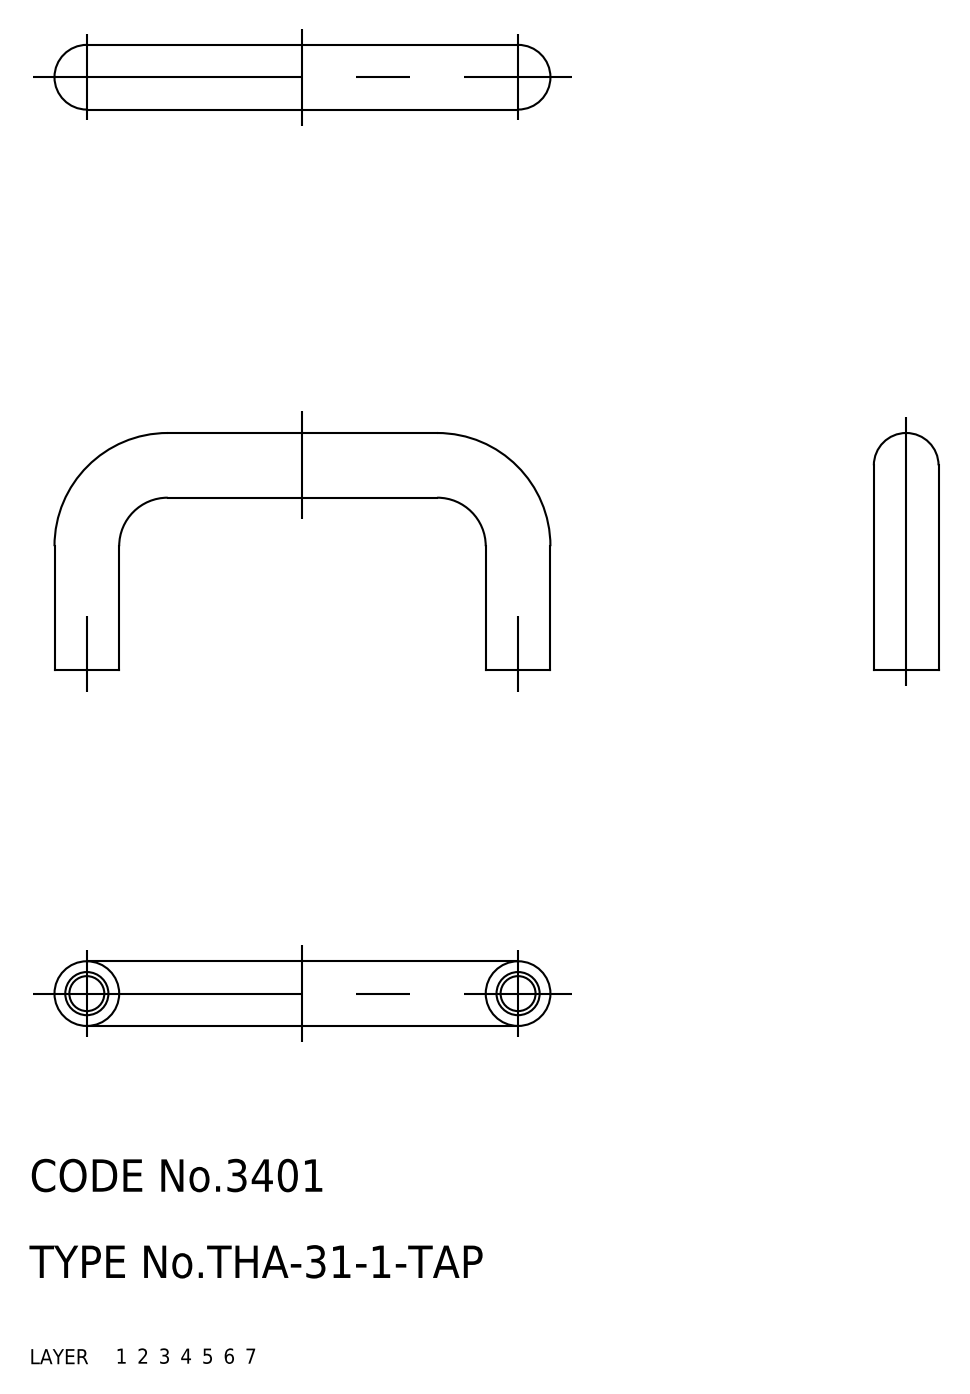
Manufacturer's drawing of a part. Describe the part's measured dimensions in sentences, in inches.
The part is named "pull". Its 3-D file was written by "CADfix (AUTOMOTIVE_DESIGN)". It is 1 solid with 10 faces: 0 planar, 0 cylindrical and 10 other. Overall it measures 1.811 by 0.866 by 0.236 inches. Its volume is 0.113 cubic inches and its surface area 2.522 square inches.
